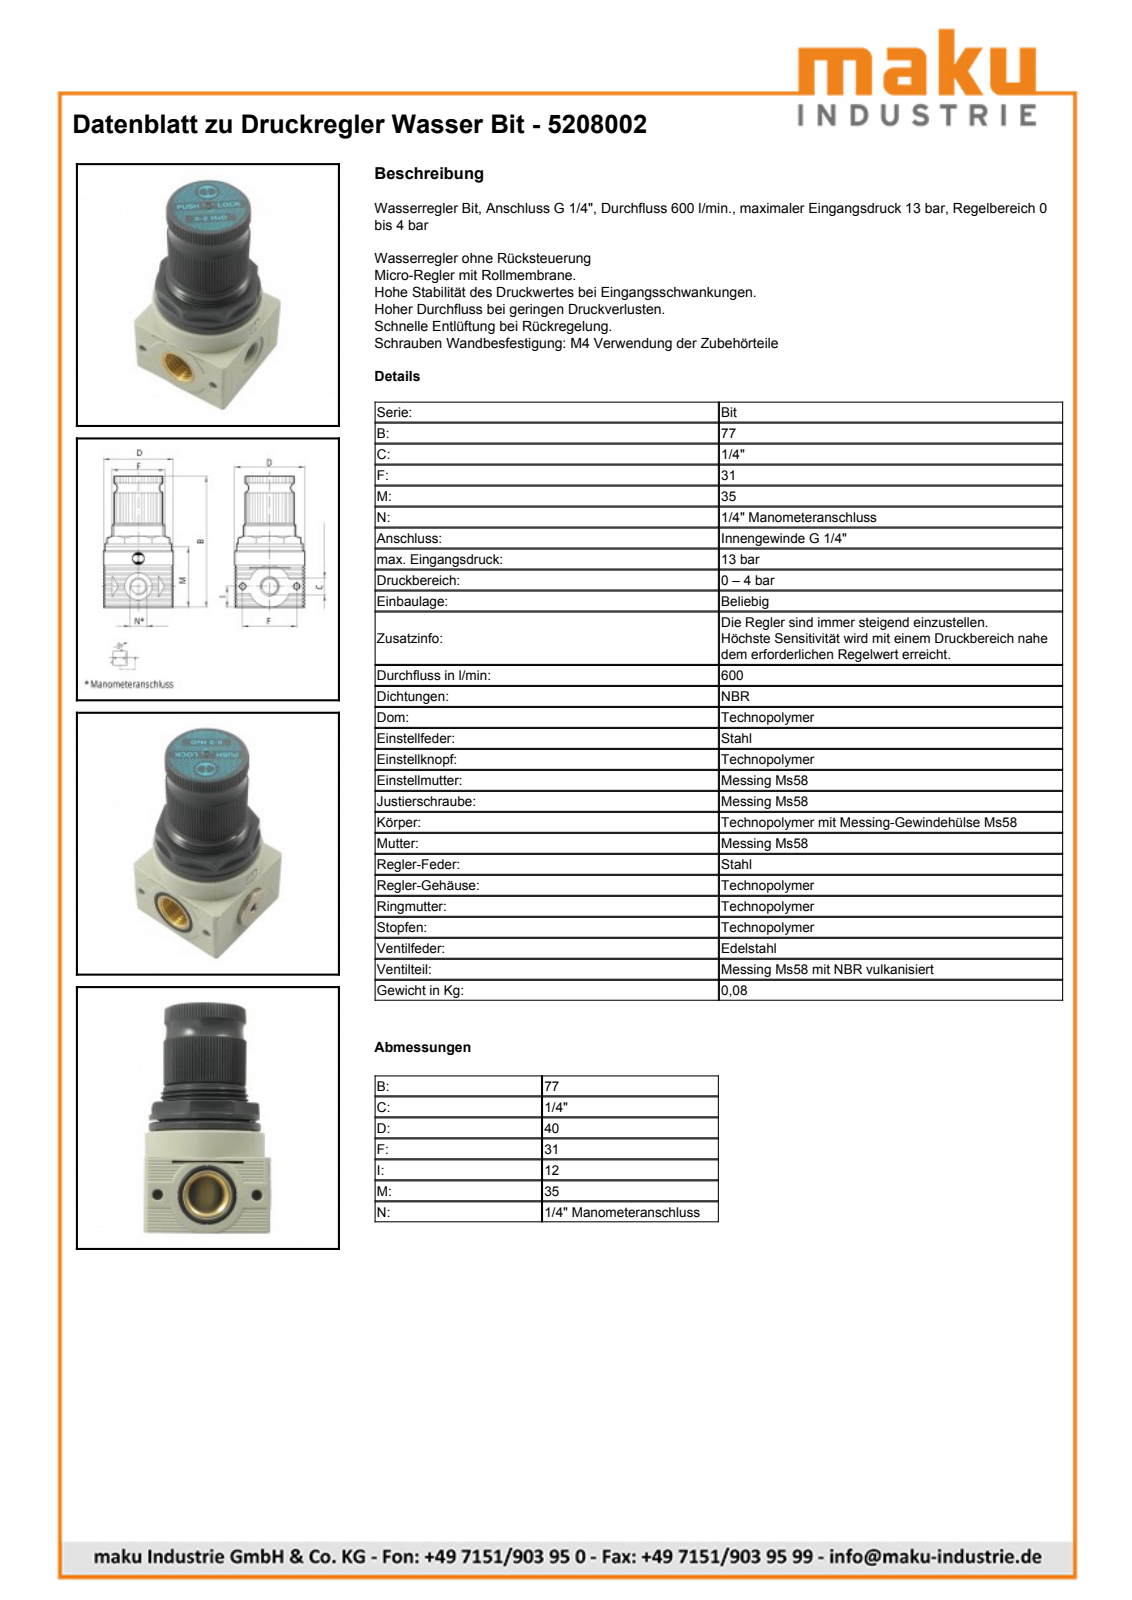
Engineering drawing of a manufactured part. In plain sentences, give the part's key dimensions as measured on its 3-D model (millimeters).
The part is named "5208002; 5208002-BD; 5208002-KN; 1/8-BIT". Its 3-D file was written by "PARTsolutions (AUTOMOTIVE_DESIGN)". It is 3 solids with 127 faces: 92 planar, 27 cylindrical and 8 other. Overall it measures 77 by 41.5 by 40 millimeters. Its volume is 76 444 cubic millimeters and its surface area 18 319 square millimeters. Round holes: 2 of diameter 4, 1 of diameter 8.57, 1 of diameter 11.45, 1 of diameter 15.5. Round bosses or shafts: 1 of diameter 39.9, 1 of diameter 38, 1 of diameter 37.6, 1 of diameter 30, 1 of diameter 28, 1 of diameter 24, 1 of diameter 15, 1 of diameter 9.73. Partial cylindrical surfaces (rounded edges, fillets, slot ends): 1 of radius 12. The main face-to-face distances are 32, 40, 1, 9, 10, 39.95, 77, 45, 39, 19. The hole center spacings are 15.5, 31.
